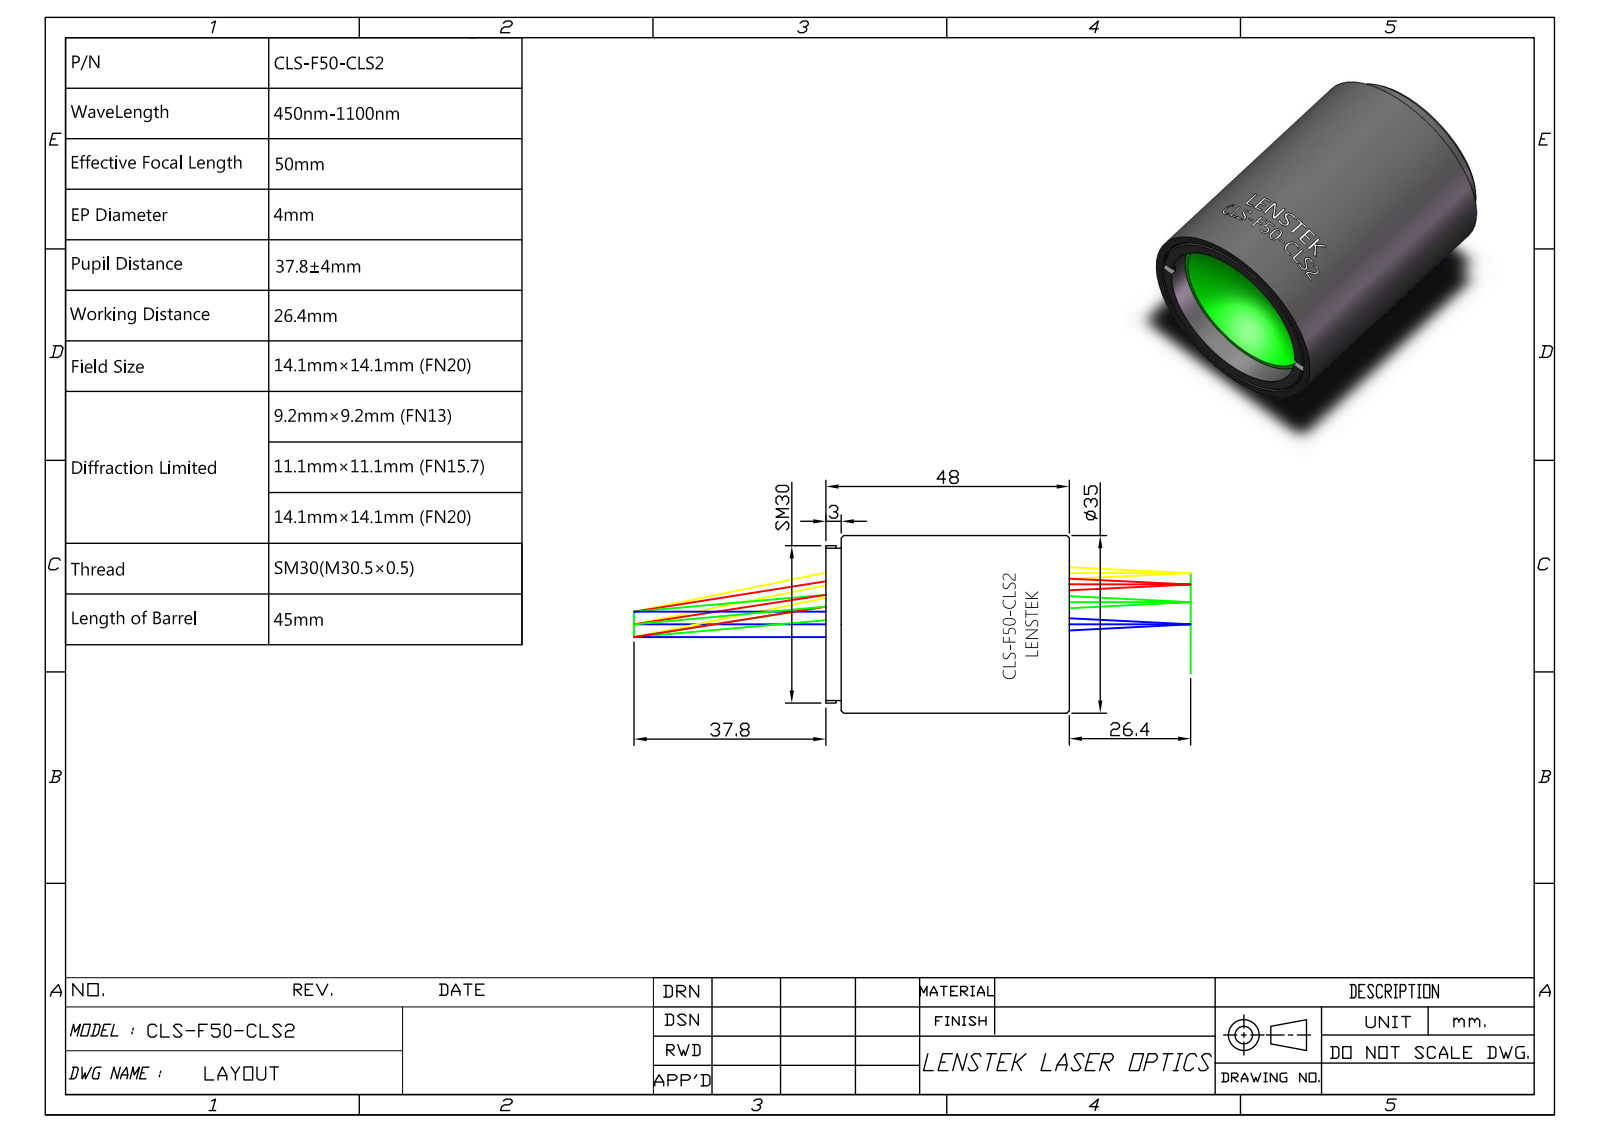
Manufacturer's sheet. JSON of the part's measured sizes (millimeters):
{"part_name": "SL50-CLS2-2; SL50-CLS2-1; SL50-CLS2-4; SL50-CLS2-3 (+1 more)", "step_written_by": "SolidWorks 2018 (AUTOMOTIVE_DESIGN)", "units": "millimeters", "bodies": {"solids": 4, "faces": 282, "planar": 126, "cylindrical": 48, "other": 108}, "overall_size": [48, 35, 35], "volume_mm3": 18529, "surface_area_mm2": 15760, "round_holes": [[26, 1], [28, 1], [29, 1], [31, 1], [32, 1], [33, 1]], "round_bosses_or_shafts": [[35, 1], [30.5, 1], [29.6, 1]], "partial_cylinders_radius": [[17.49, 1]], "face_to_face_distances": [39.94, 3.62, 43.56, 1.44, 41.38, 45, 3, 4.44, 44.38, 48]}
